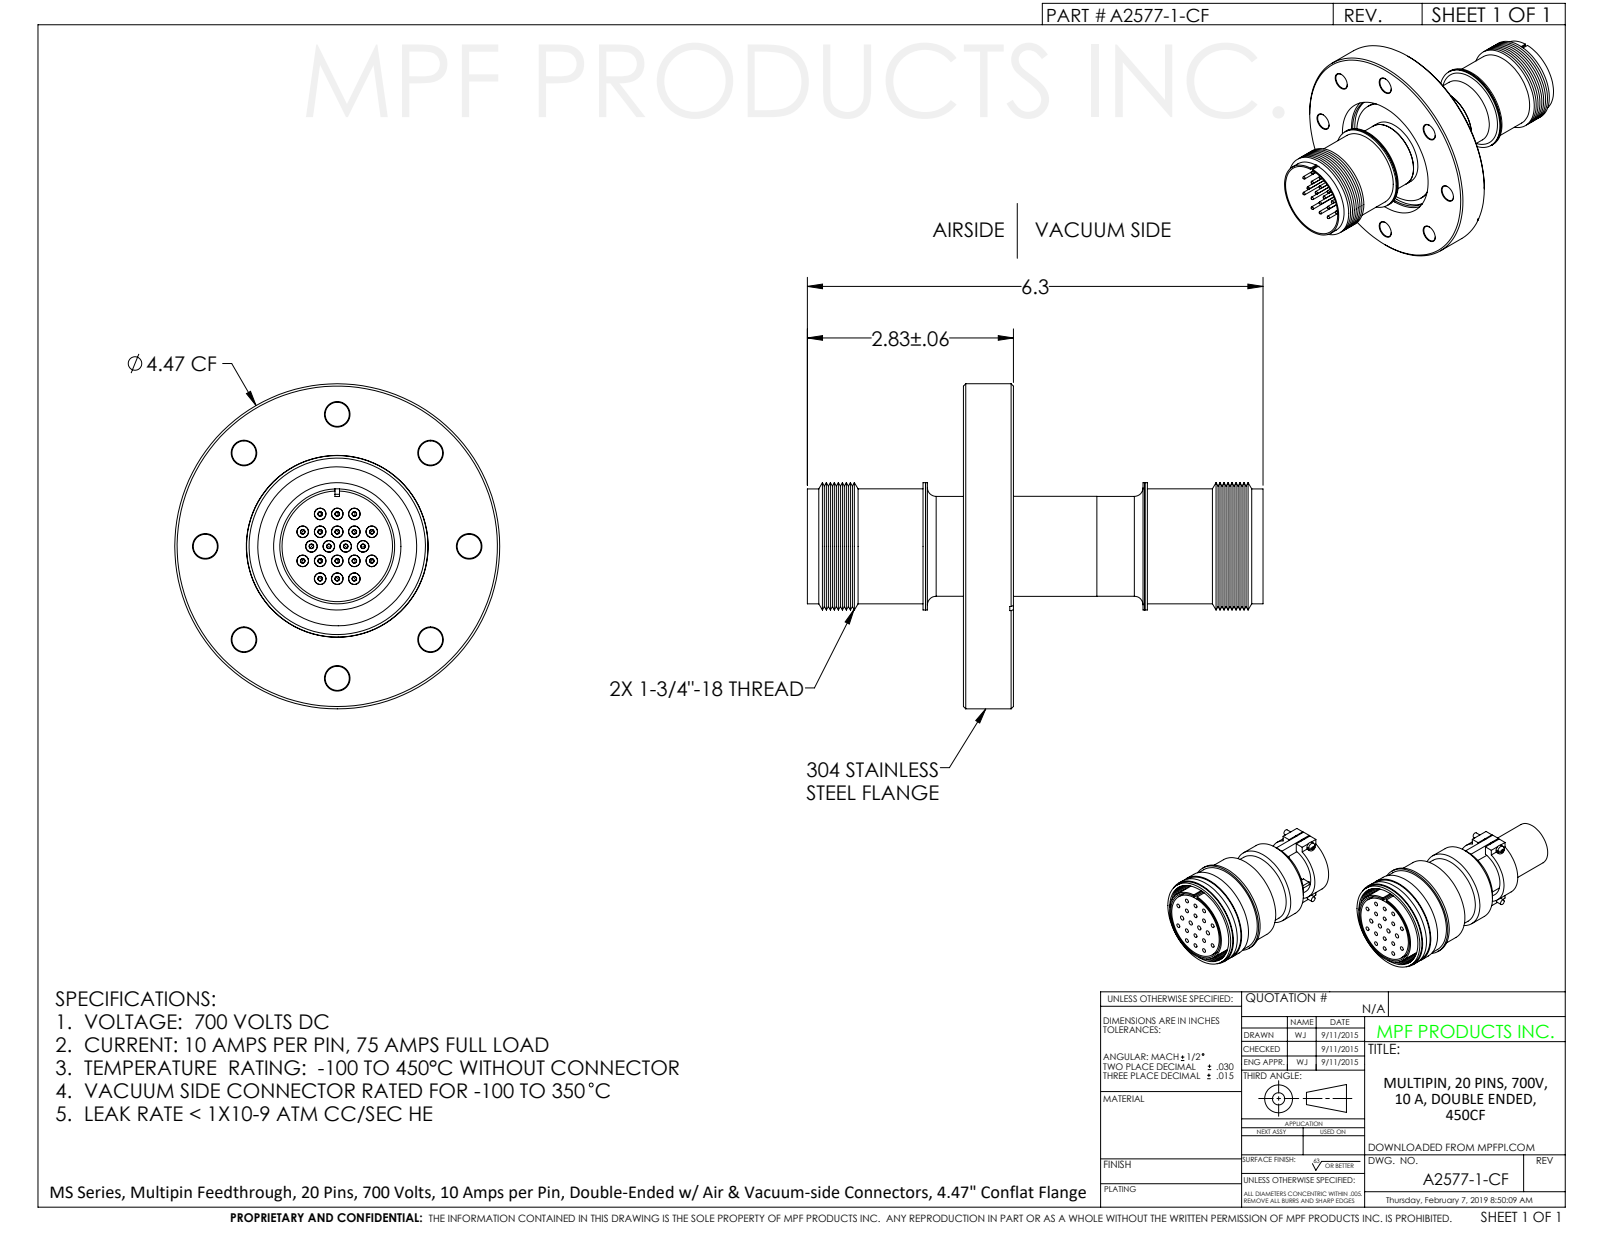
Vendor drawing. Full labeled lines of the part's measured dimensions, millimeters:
Part name (STEP PRODUCT): A2577-1-CF
STEP written by: SolidWorks 2012 (CONFIG_CONTROL_DESIGN)
Units: millimetres
Bodies: 1 solid, 946 faces (205 planar, 535 cylindrical, 206 other)
Overall size (bounding box): 159.1 × 113.5 × 113.5
Volume: 168 800 mm³ · Surface area: 100 800 mm²
Round holes (diameter × count): ⌀8.4 ×8, ⌀1.8 ×4, ⌀32.1 ×1, ⌀33.3 ×1, ⌀38.6 ×1, ⌀39.4 ×1, ⌀61.6 ×1, ⌀63.1 ×1, ⌀77.2 ×1, ⌀82.6 ×1
Round bosses / shafts (diameter × count): ⌀4.3 ×24, ⌀4.7 ×20, ⌀1.4 ×20, ⌀113.5 ×1, ⌀55.5 ×1, ⌀44.5 ×1, ⌀40.7 ×1, ⌀40.1 ×1
Main face-to-face distances: 17.3, 16, 1.3, 1.3, 102, 6.5, 9.5, 10.8, 1, 31.4
Hole centre spacings: 46.1, 65.2, 85.1, 14.1, 28.2, 33.5, 35.3, 35.3
